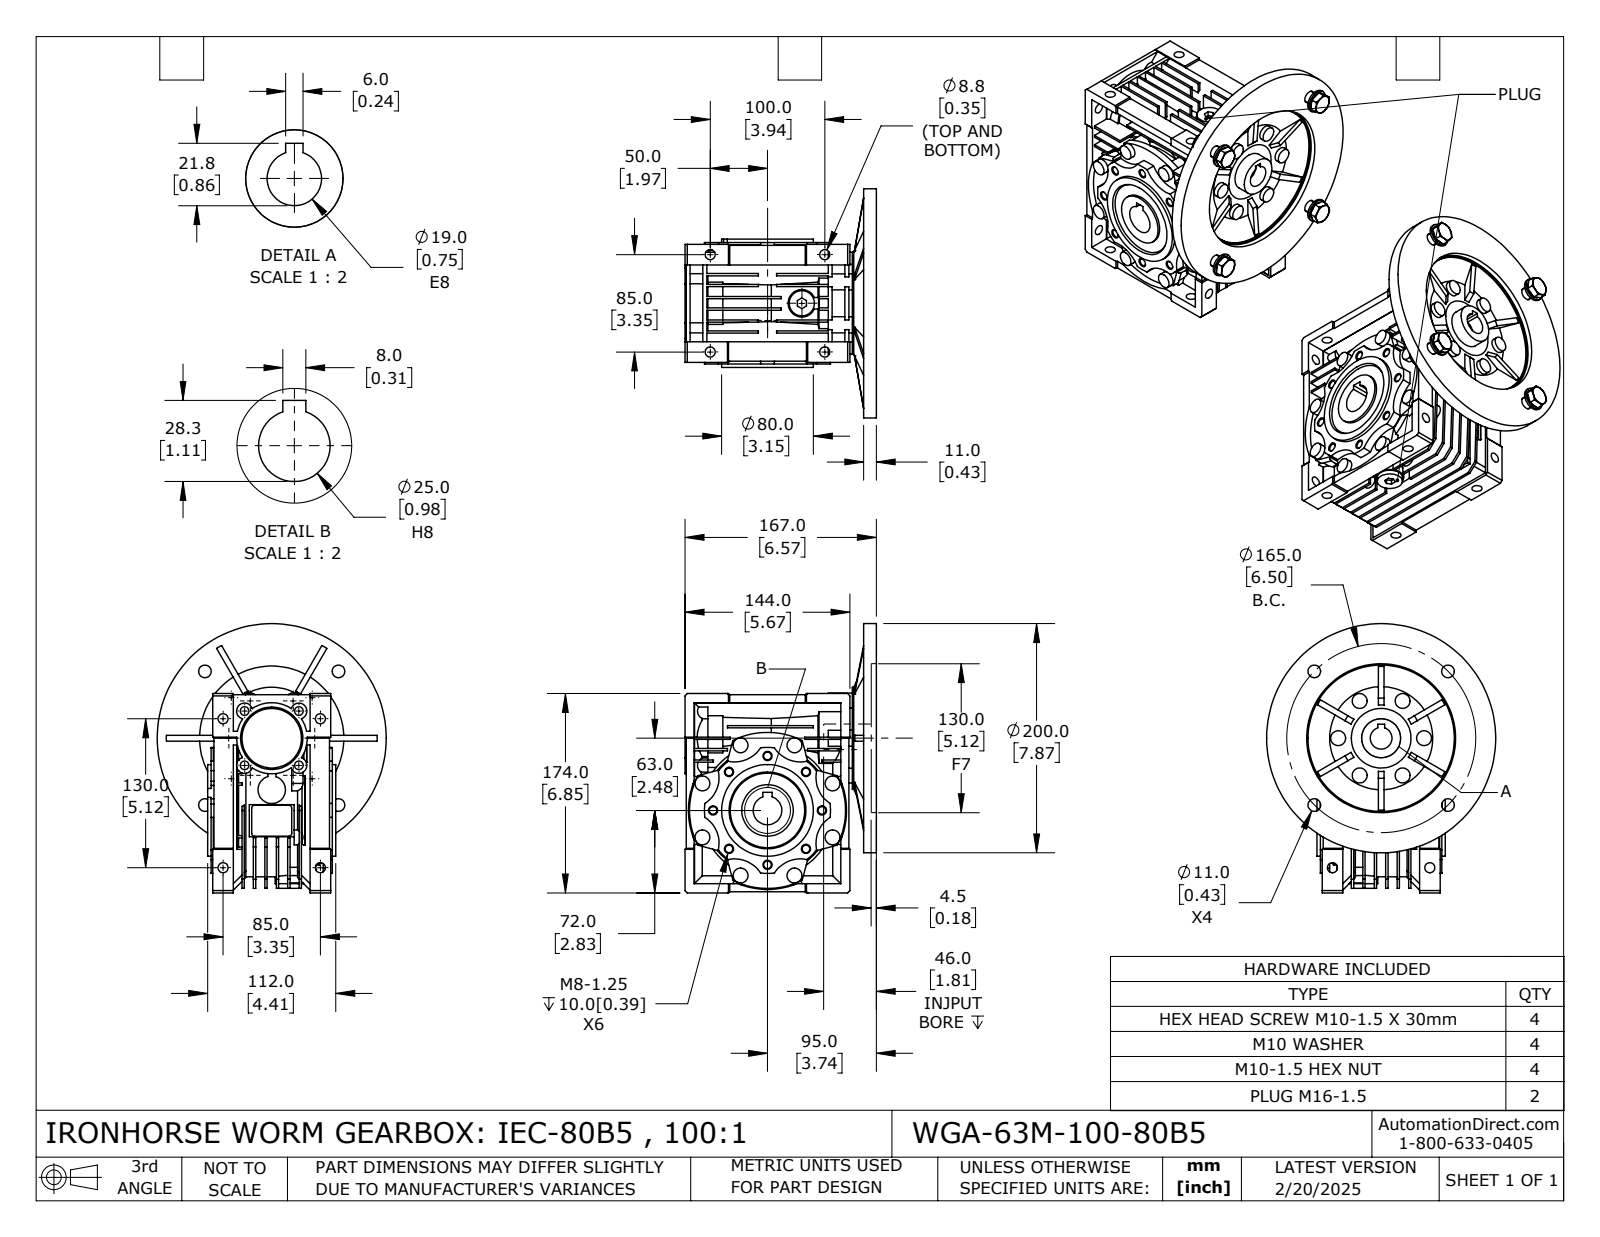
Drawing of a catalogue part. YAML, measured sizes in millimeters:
part_name: "WGA-63M-100-80B5"
step_written_by: "SolidWorks 2024 (CONFIG_CONTROL_DESIGN)"
units: millimeters
bodies: {solids: 20, faces: 1529, planar: 897, cylindrical: 394, other: 238}
overall_size: [235, 200, 183.43]
volume: 2032000
surface_area: 401437
round_holes:
  - {diameter: 6.65, count: 8}
  - {diameter: 8.78, count: 8}
  - {diameter: 7.56, count: 4}
  - {diameter: 8.5, count: 4}
  - {diameter: 10, count: 4}
  - {diameter: 10.5, count: 4}
  - {diameter: 11, count: 4}
  - {diameter: 14.5, count: 2}
  - {diameter: 19, count: 1}
  - {diameter: 20, count: 1}
  - {diameter: 25, count: 1}
  - {diameter: 34, count: 1}
round_bosses_or_shafts:
  - {diameter: 13, count: 14}
  - {diameter: 20, count: 4}
  - {diameter: 16, count: 4}
  - {diameter: 24, count: 3}
  - {diameter: 22, count: 2}
  - {diameter: 15.8, count: 2}
  - {diameter: 13.7, count: 2}
  - {diameter: 200, count: 1}
partial_cylinders:
  - {radius: 7, count: 10}
  - {radius: 27, count: 8}
  - {radius: 2.5, count: 4}
  - {radius: 8.35, count: 1}
  - {radius: 29.5, count: 1}
  - {radius: 30.5, count: 1}
  - {radius: 42, count: 1}
  - {radius: 46, count: 1}
face_to_face_distances: [10, 8, 20, 2, 11, 30, 12, 7, 40, 18]
hole_center_spacings: [36.36, 47.5, 67.18, 87.77, 89.05, 33.5, 47.38, 49]
